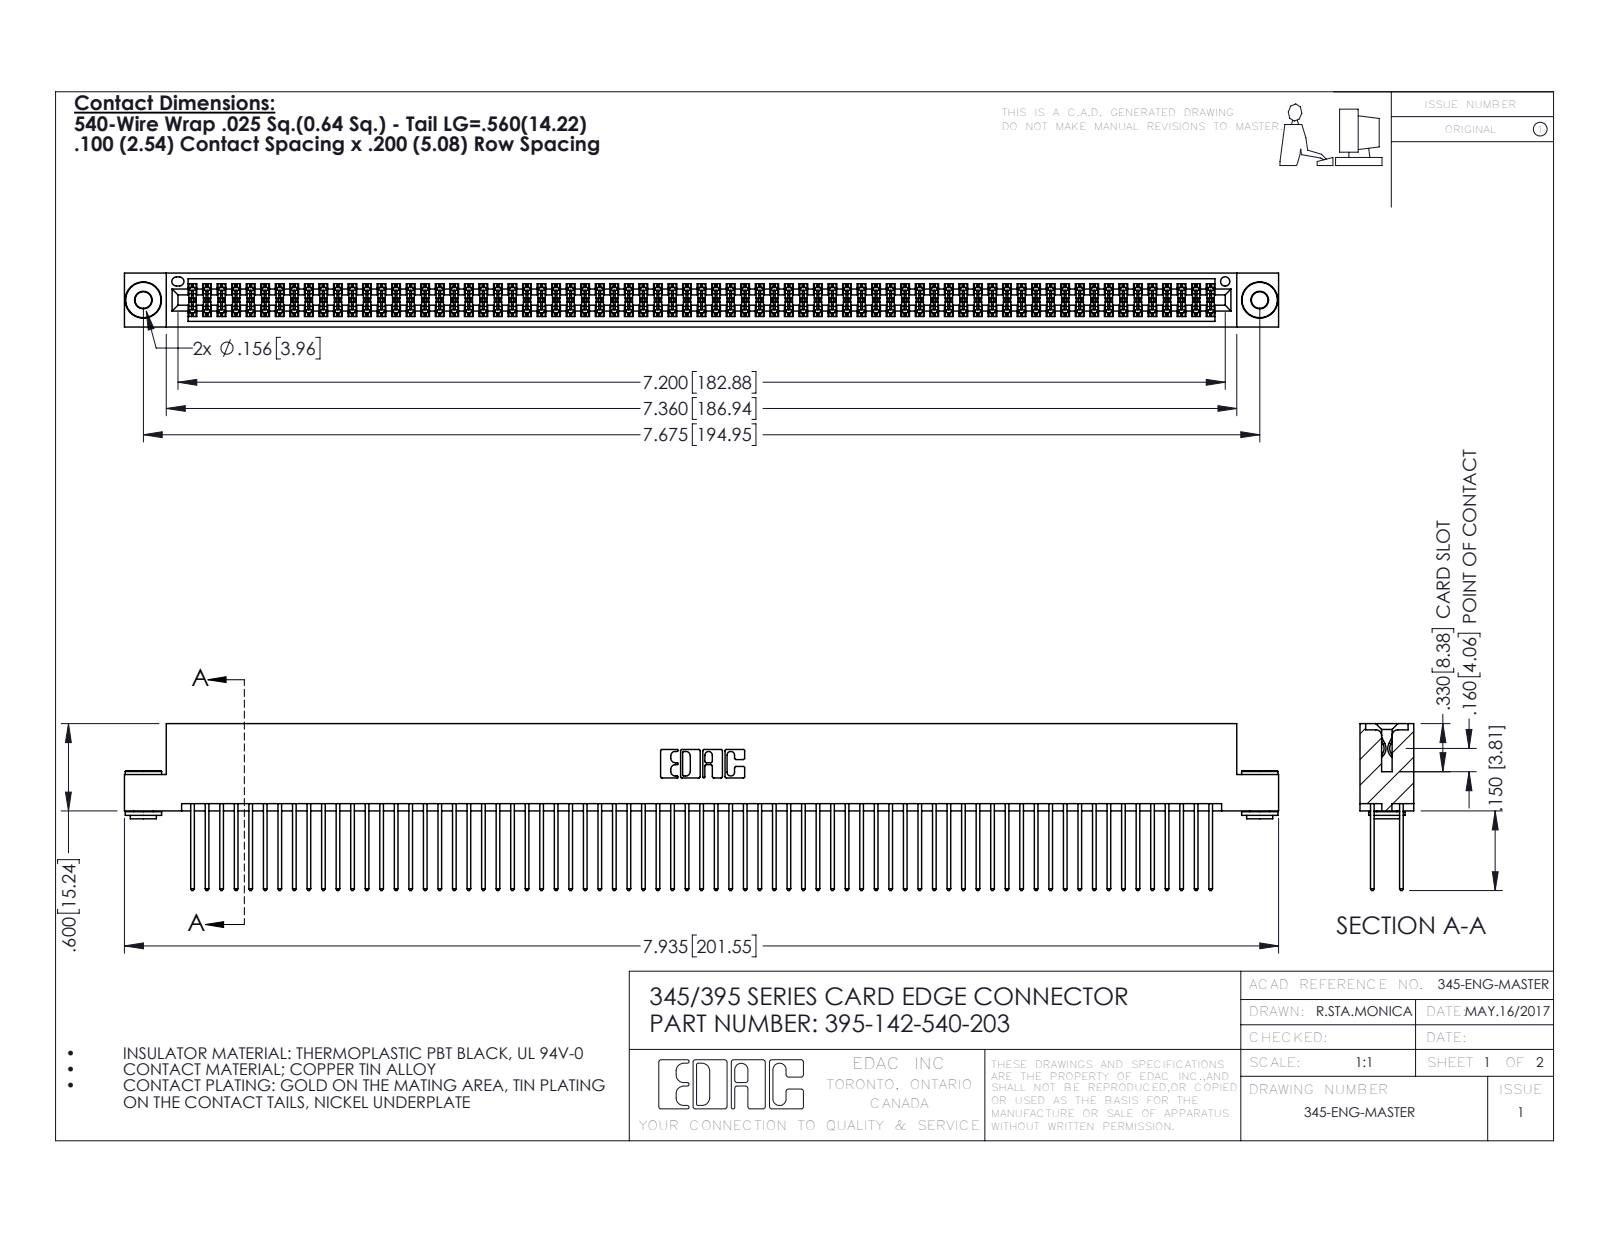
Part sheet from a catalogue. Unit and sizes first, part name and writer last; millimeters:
Units: millimetres
Overall size (bounding box): 201.5 × 29.1 × 9.4
Round holes (diameter × count): ⌀2.9 ×2, ⌀4 ×2, ⌀1.6 ×1
Round bosses / shafts (diameter × count): ⌀6.4 ×2, ⌀4.6 ×2, ⌀3.5 ×2
Partial cylindrical surfaces — rounded edges, fillets, slot ends (radius × count): R0.2 ×213, R0.3 ×142, R0.3 ×22, R0.2 ×6, R0.8 ×6, R0.7 ×3, R0.4 ×2, R0.5 ×2
Main face-to-face distances: 1.8, 7.6, 5.1, 0.6, 2.5, 6.9, 5.7, 9.4, 4.4, 3.8
Hole centre spacings: 6.9, 189, 194.9
Volume: 20 400 mm³ · Surface area: 33 430 mm²
Bodies: 145 solids, 7264 faces (4776 planar, 2480 cylindrical, 8 other)
Part name (STEP PRODUCT): 395-142-540-203; 345 Part_Flush Mounting Lugs - 0.156 Dia-TH; 345-250-002_345-250-002-102; 345-292-001_345-293-140
STEP written by: SolidWorks 2016 (CONFIG_CONTROL_DESIGN)
